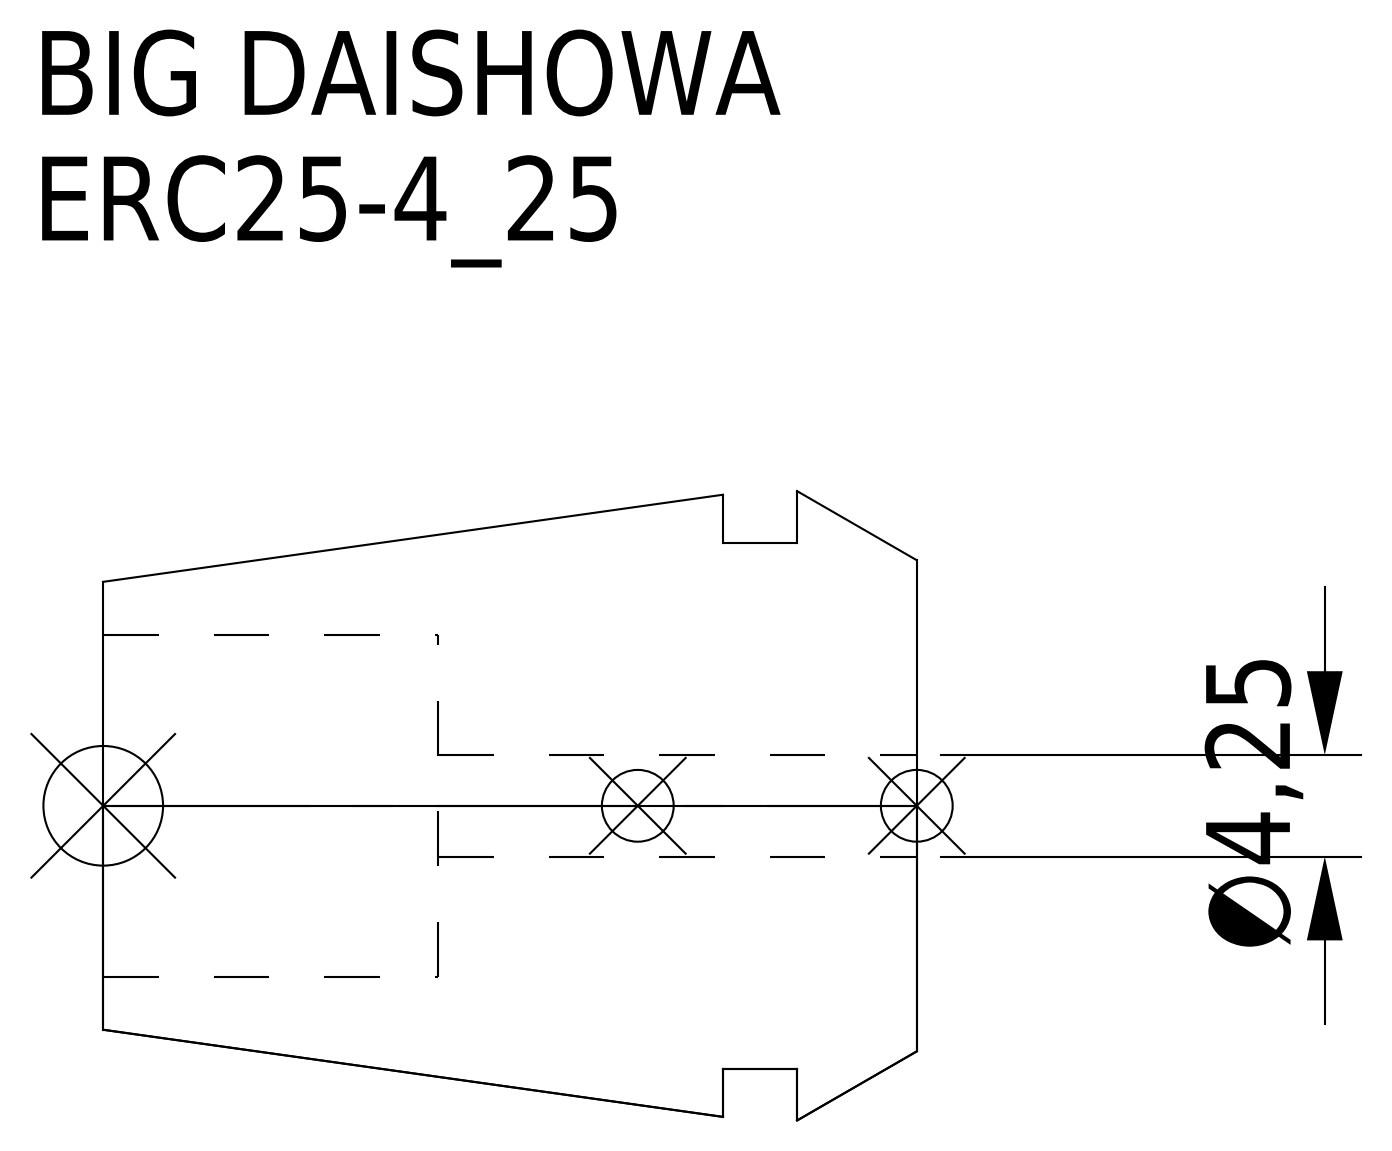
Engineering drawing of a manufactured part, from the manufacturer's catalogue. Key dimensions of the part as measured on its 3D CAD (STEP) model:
Part name (STEP PRODUCT): ERC25-4_25
STEP written by: CREO PARAMETRIC BY PTC INC, 2016380 (AUTOMOTIVE_DESIGN)
Units: millimetres
Bodies: 1 solid, 15 faces (5 planar, 6 cylindrical, 4 other)
Overall size (bounding box): 34 × 26.3 × 26.3
Volume: 11 071 mm³ · Surface area: 4 264 mm²
Round holes (diameter × count): ⌀4.25 ×1, ⌀14.3 ×1
Round bosses / shafts (diameter × count): ⌀22 ×1
Main face-to-face distances: 5, 8.1, 3.1, 20, 15, 11.9, 34, 29, 25.9, 14
